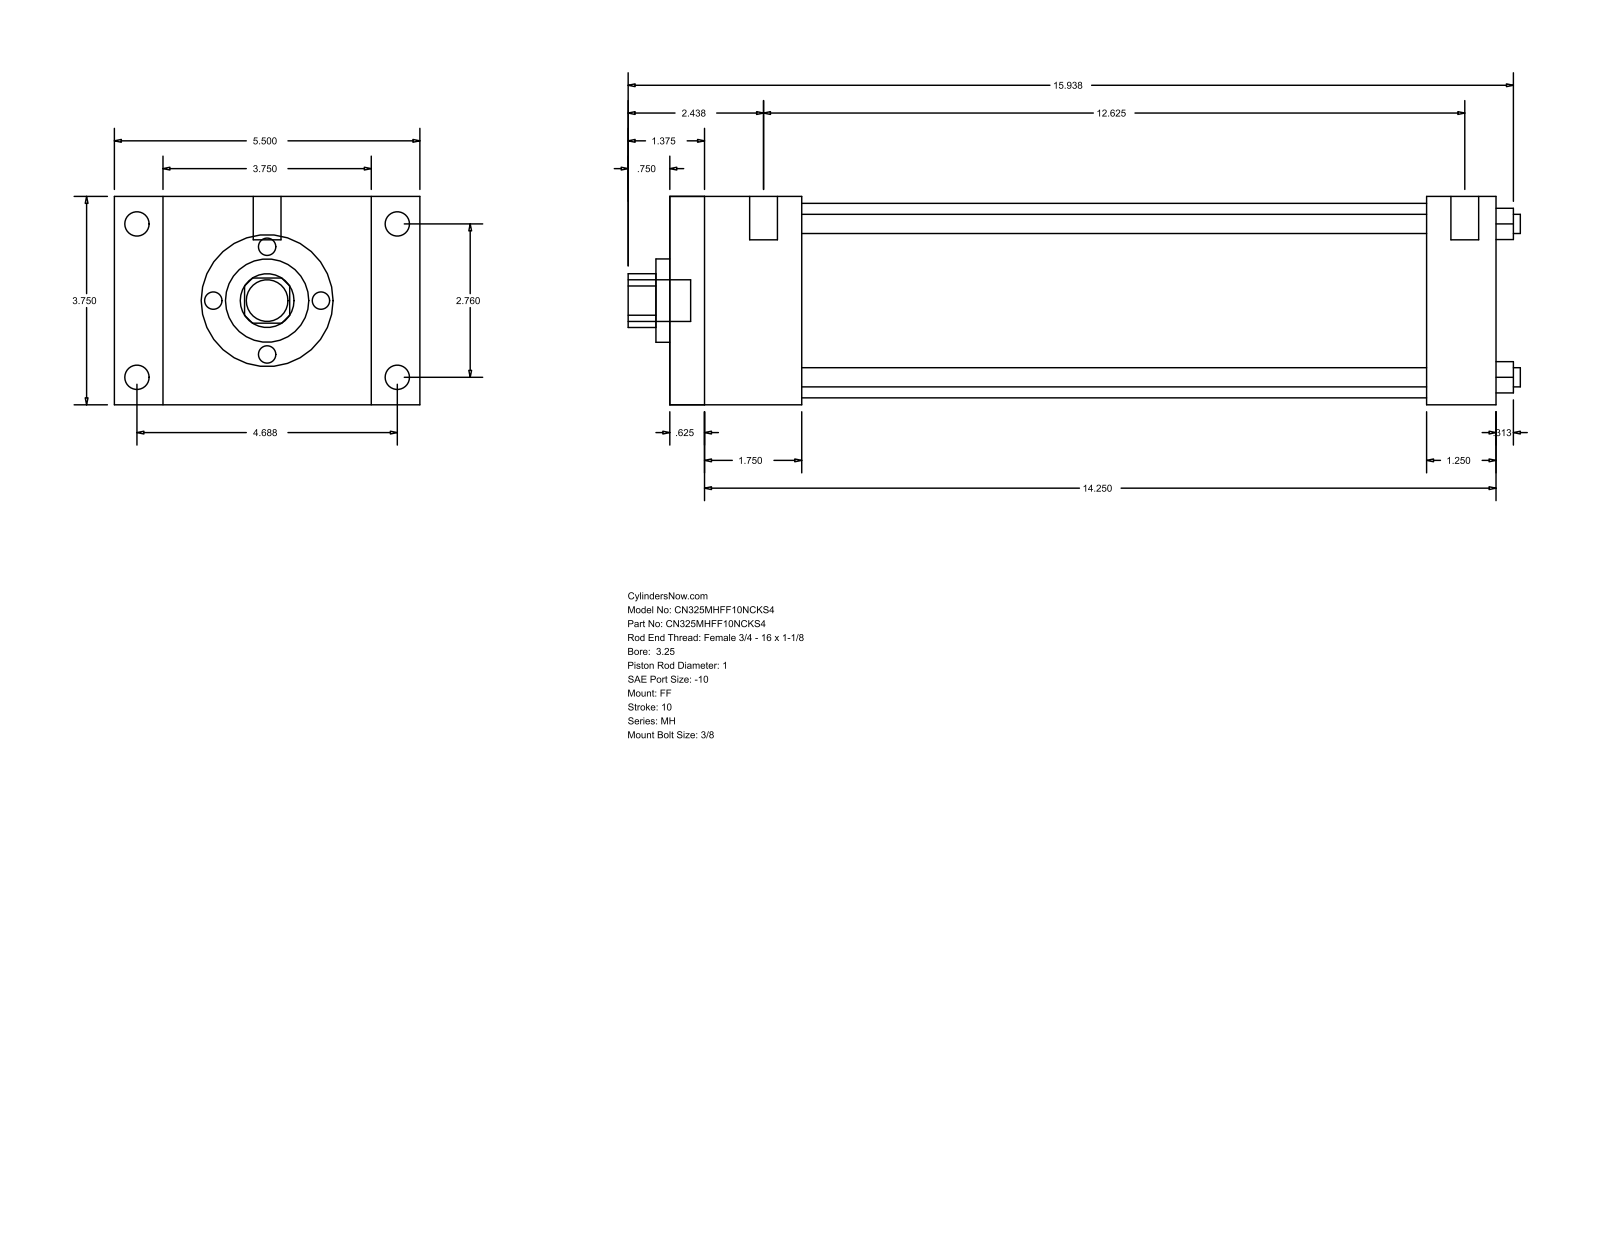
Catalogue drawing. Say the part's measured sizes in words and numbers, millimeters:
The part is named "MH_FF__0325_1". Its 3-D file was written by "GSSL Pune (CONFIG_CONTROL_DESIGN)". It is 0 solids with 92 faces: 64 planar, 28 cylindrical and 0 other. Overall it measures 407.99 by 139.7 by 95.25 millimeters. Round holes: 4 of diameter 8.76, 1 of diameter 25.4, 1 of diameter 38.1, 1 of diameter 88.9. Round bosses or shafts: 4 of diameter 11.13, 4 of diameter 5.56, 2 of diameter 12.7, 1 of diameter 19.05. Partial cylindrical surfaces (rounded edges, fillets, slot ends): 1 of radius 12.29. The main face-to-face distances are 95.24, 377.83, 15.87, 361.96, 22.23, 117.47, 346.07, 330.2, 31.76, 60.33. The hole center spacings are 49.57, 70.1, 99.14.
